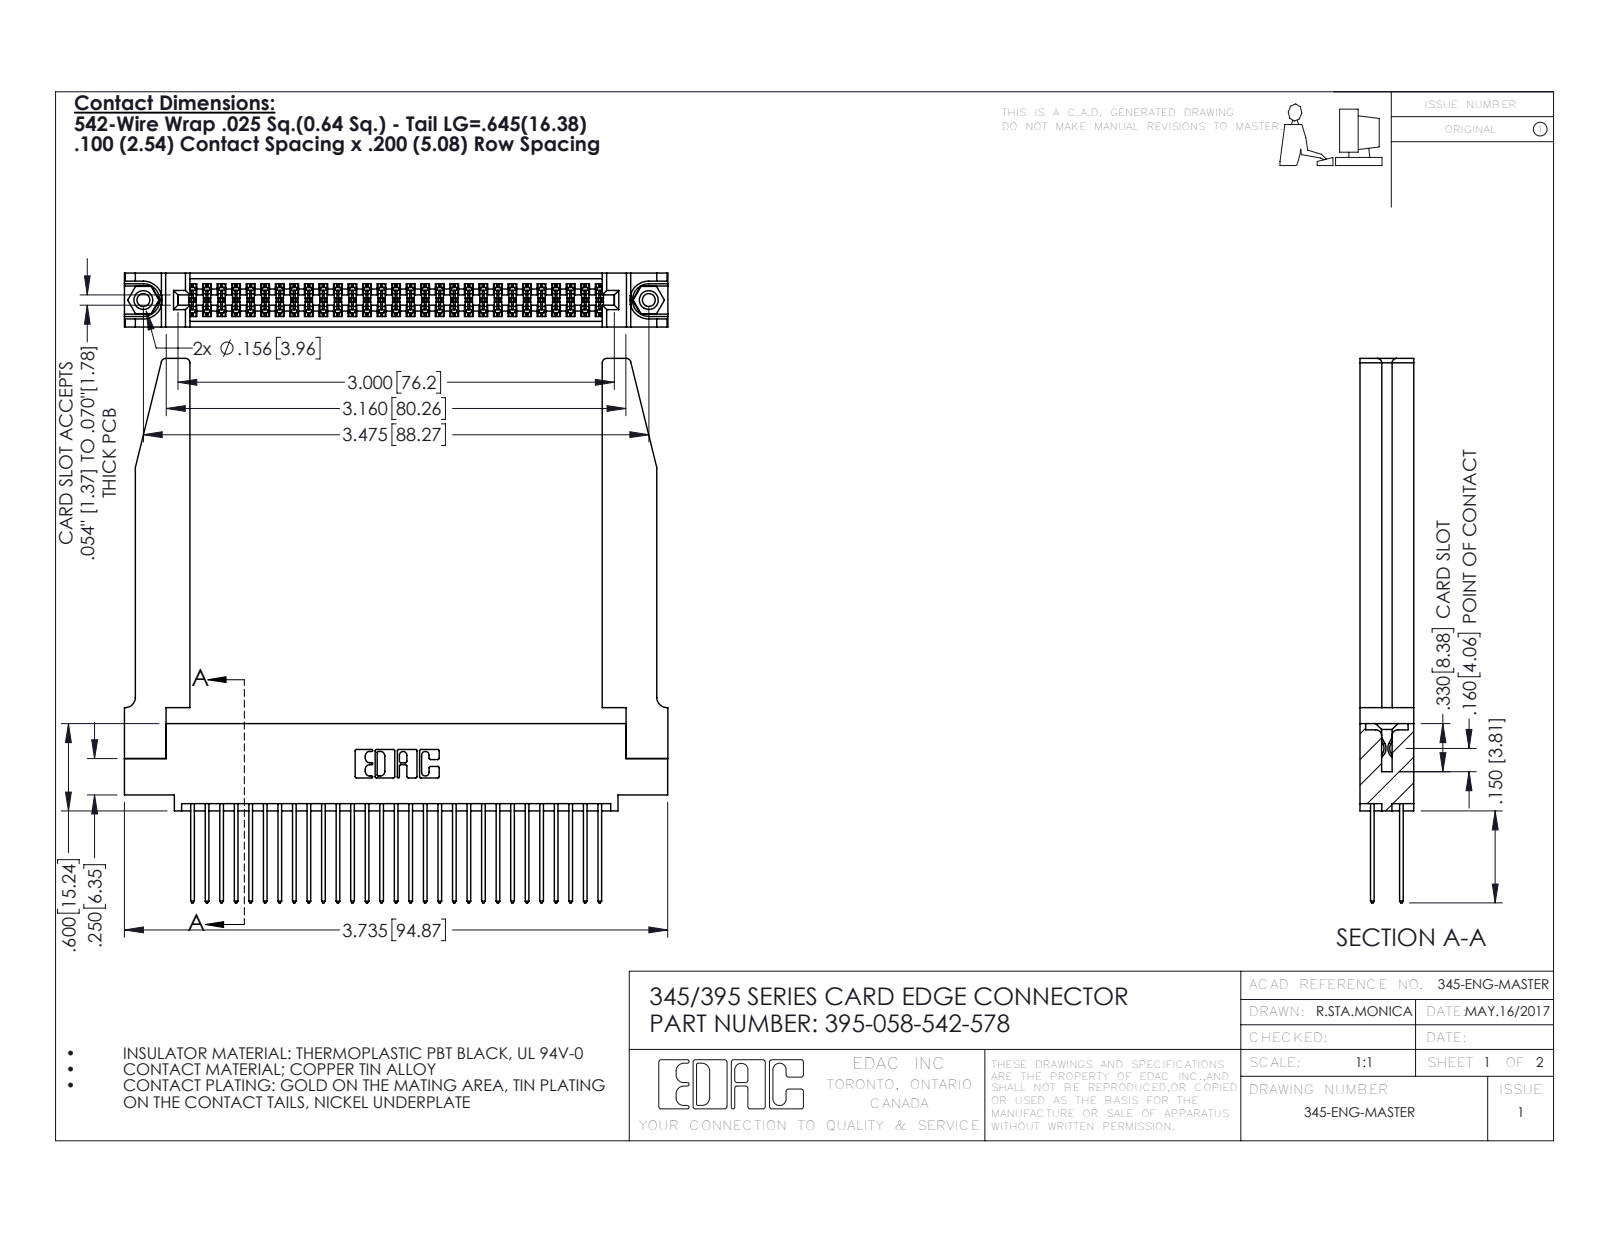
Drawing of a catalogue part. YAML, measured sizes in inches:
part_name: "345 Part_0.110 Offset - 0.156 Dia-TH; 395-058-542-578; 345-220-078_345-220-078; 345-292-001_345-293-142 (+1 more)"
step_written_by: "SolidWorks 2016 (CONFIG_CONTROL_DESIGN)"
units: inches
bodies: {solids: 63, faces: 3264, planar: 2140, cylindrical: 1072, other: 52}
overall_size: [3.742, 3.736, 0.37]
volume: 1.041
surface_area: 33.61
round_holes:
  - {diameter: 0.089, count: 2}
  - {diameter: 0.125, count: 2}
  - {diameter: 0.156, count: 2}
  - {diameter: 0.064, count: 1}
round_bosses_or_shafts:
  - {diameter: 0.155, count: 2}
partial_cylinders:
  - {radius: 0.006, count: 87}
  - {radius: 0.01, count: 58}
  - {radius: 0.01, count: 22}
  - {radius: 0.03, count: 8}
  - {radius: 0.007, count: 6}
  - {radius: 0.031, count: 6}
  - {radius: 0.026, count: 3}
  - {radius: 0.014, count: 2}
face_to_face_distances: [0.072, 0.37, 0.298, 0.2, 0.098, 0.272, 0.025, 0.225, 0.175, 0.148]
hole_center_spacings: [0.27, 3.24, 3.475]
